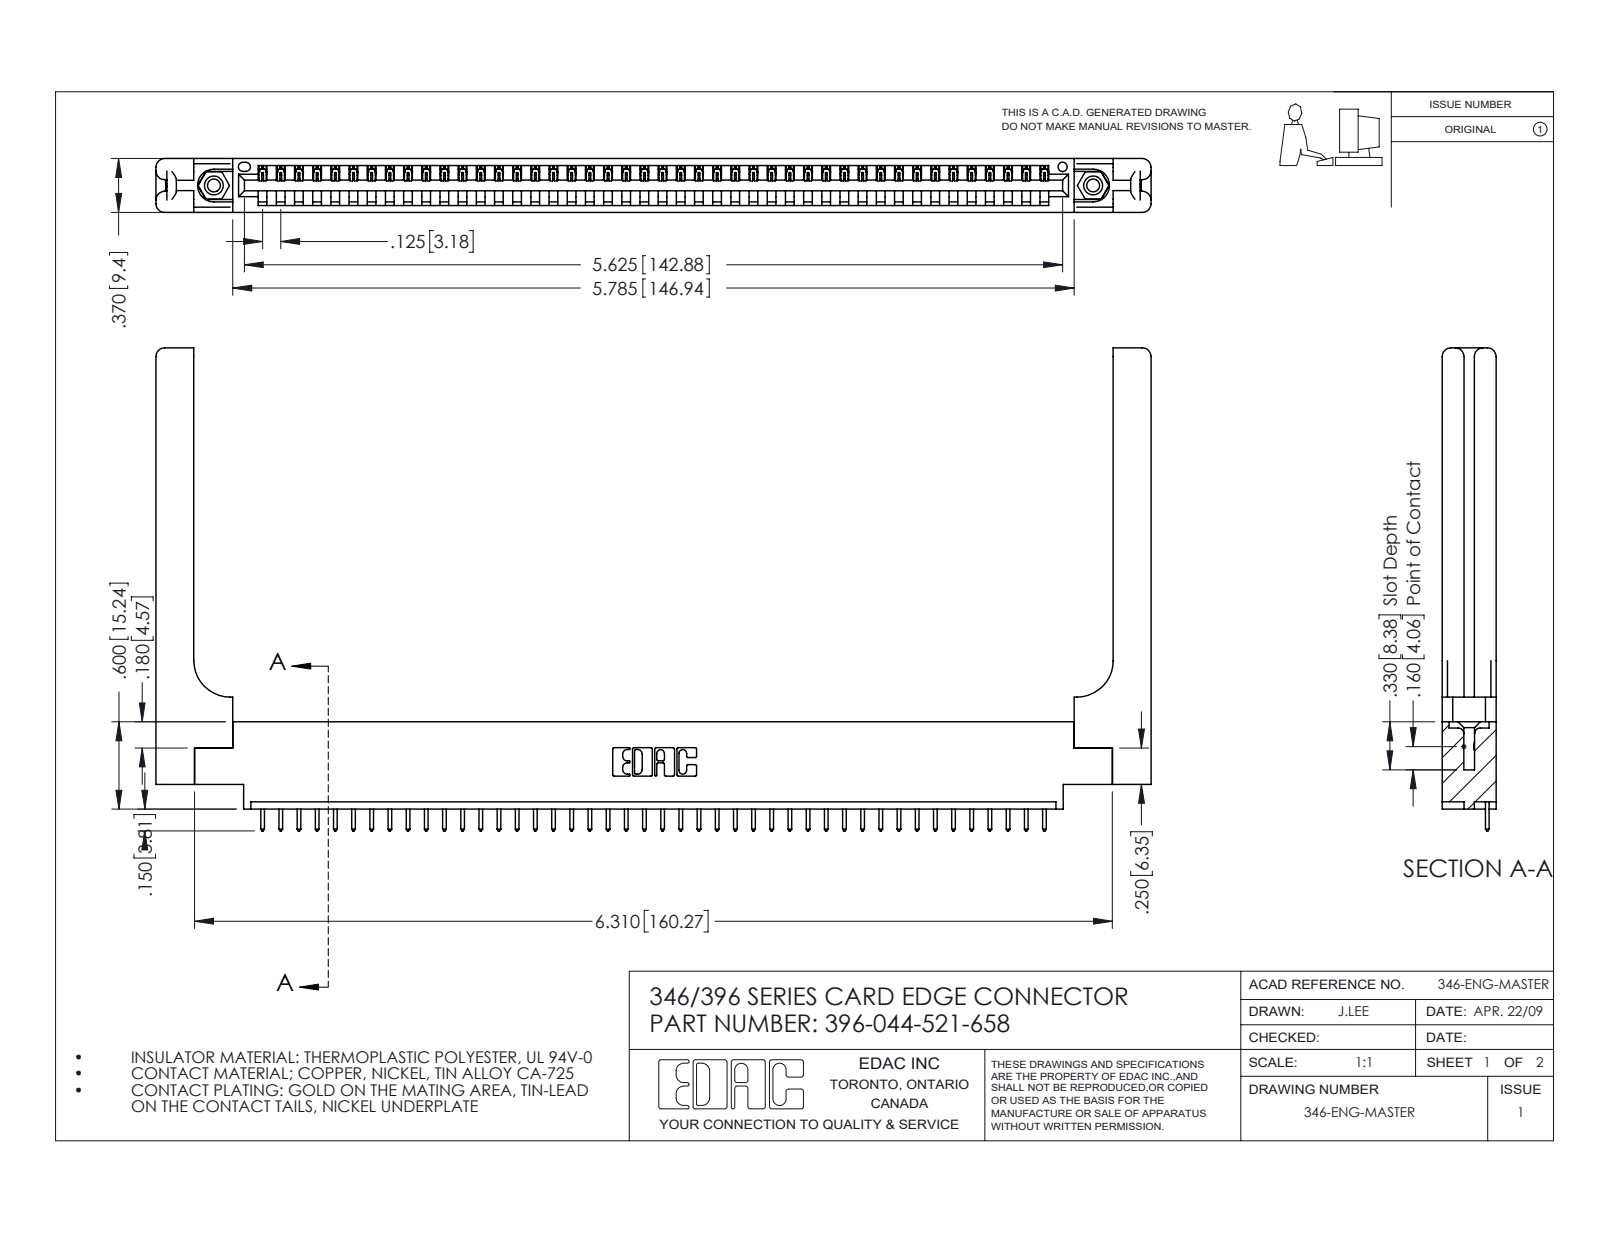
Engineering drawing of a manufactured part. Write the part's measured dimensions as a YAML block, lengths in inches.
part_name: "345-292-001_345-293-121; 346 Part_0.170 Offset - 0.156 Dia-TH; 345-250-001_345-250-001-102; 346-220-058_345-220-058 (+1 more)"
step_written_by: "SolidWorks 2016 (CONFIG_CONTROL_DESIGN)"
units: inches
bodies: {solids: 49, faces: 2934, planar: 1988, cylindrical: 886, other: 60}
overall_size: [6.841, 3.32, 0.37]
volume: 1.458
surface_area: 39.23
round_holes:
  - {diameter: 0.089, count: 2}
  - {diameter: 0.125, count: 2}
  - {diameter: 0.156, count: 2}
  - {diameter: 0.064, count: 1}
round_bosses_or_shafts:
  - {diameter: 0.155, count: 2}
partial_cylinders:
  - {radius: 0.006, count: 88}
  - {radius: 0.01, count: 88}
  - {radius: 0.01, count: 22}
  - {radius: 0.06, count: 16}
  - {radius: 0.007, count: 6}
  - {radius: 0.031, count: 6}
  - {radius: 0.026, count: 3}
  - {radius: 0.03, count: 2}
face_to_face_distances: [0.37, 0.048, 0.322, 0.072, 0.148, 0.15, 0.25, 0.298, 0.025, 0.222]
hole_center_spacings: [0.246, 5.836, 6.045]
